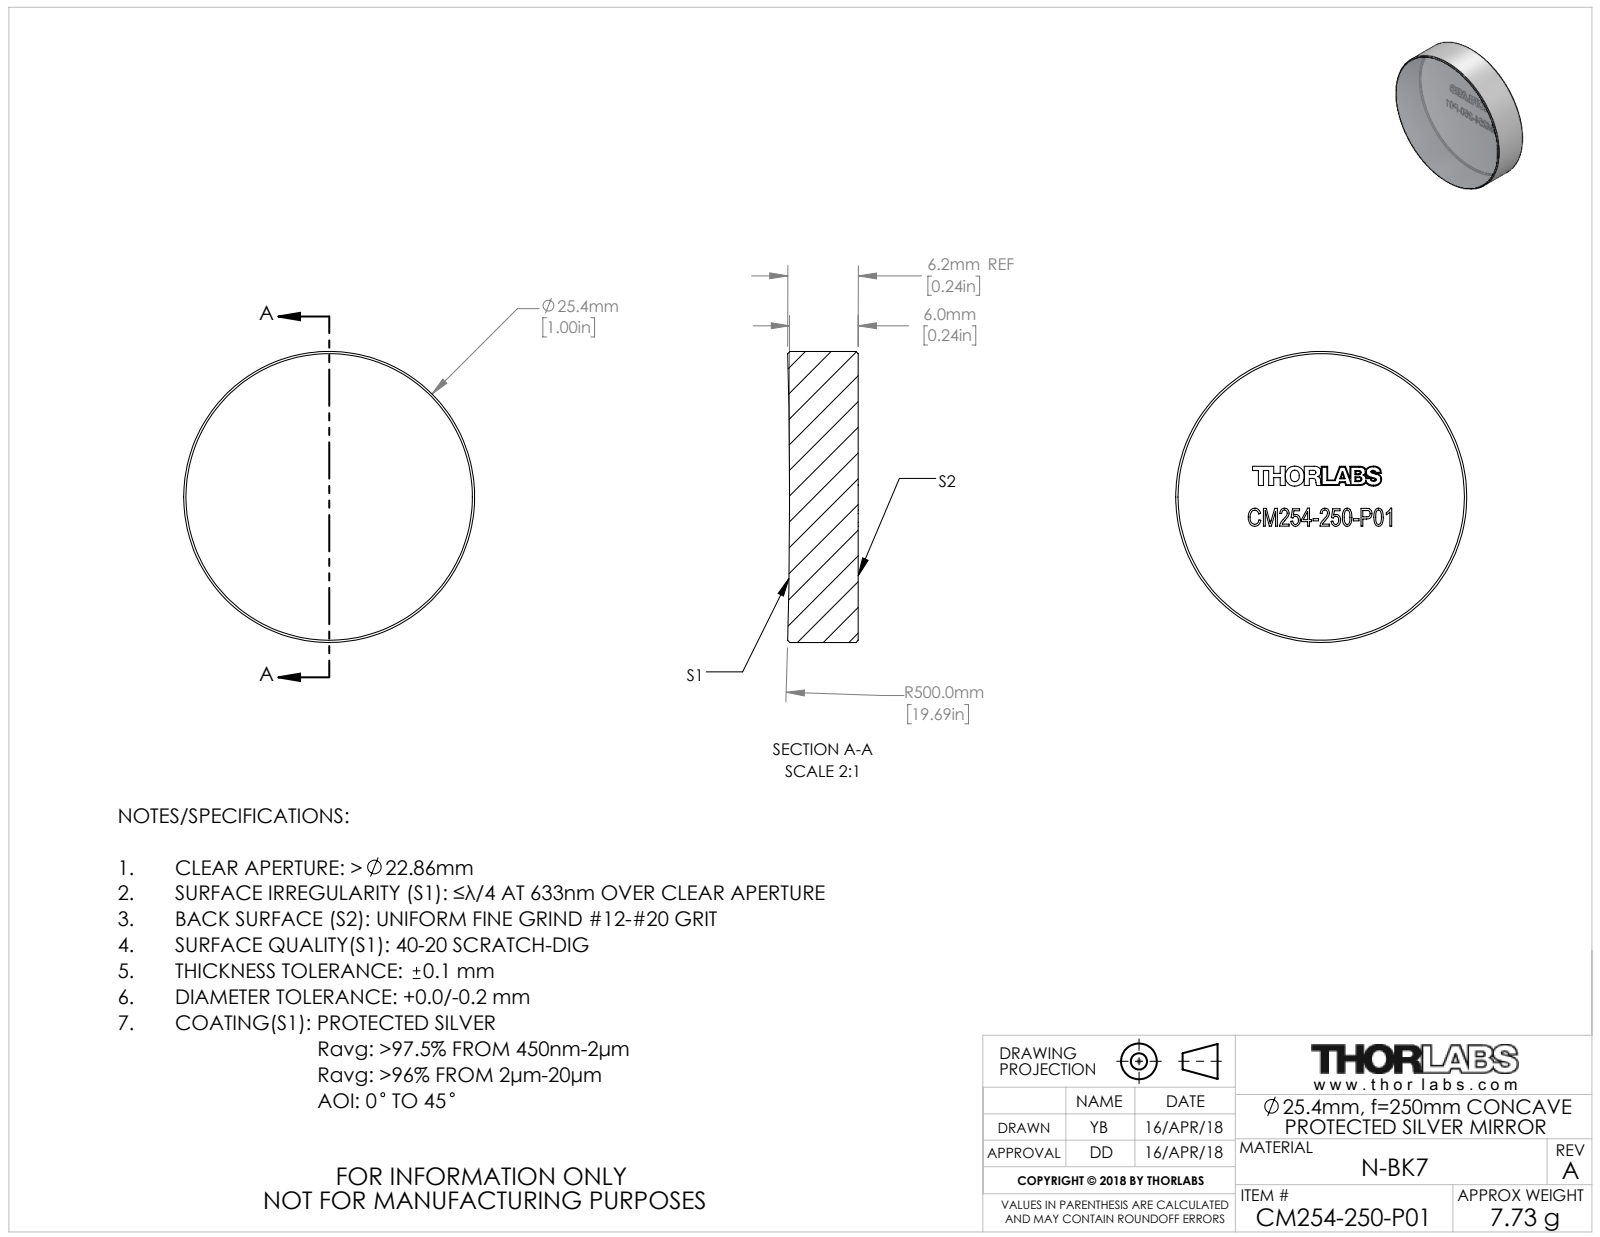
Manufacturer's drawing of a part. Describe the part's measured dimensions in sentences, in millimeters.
The part is named "TTN153295-E0W". Its 3-D file was written by "SolidWorks 2018 (CONFIG_CONTROL_DESIGN)". It is 1 solid with 41 faces: 33 planar, 2 cylindrical and 6 other. Overall it measures 25.4 by 25.4 by 6.16 millimeters. Its volume is 3 078 cubic millimeters and its surface area 1 486 square millimeters. Round bosses or shafts: 1 of diameter 25.4.
